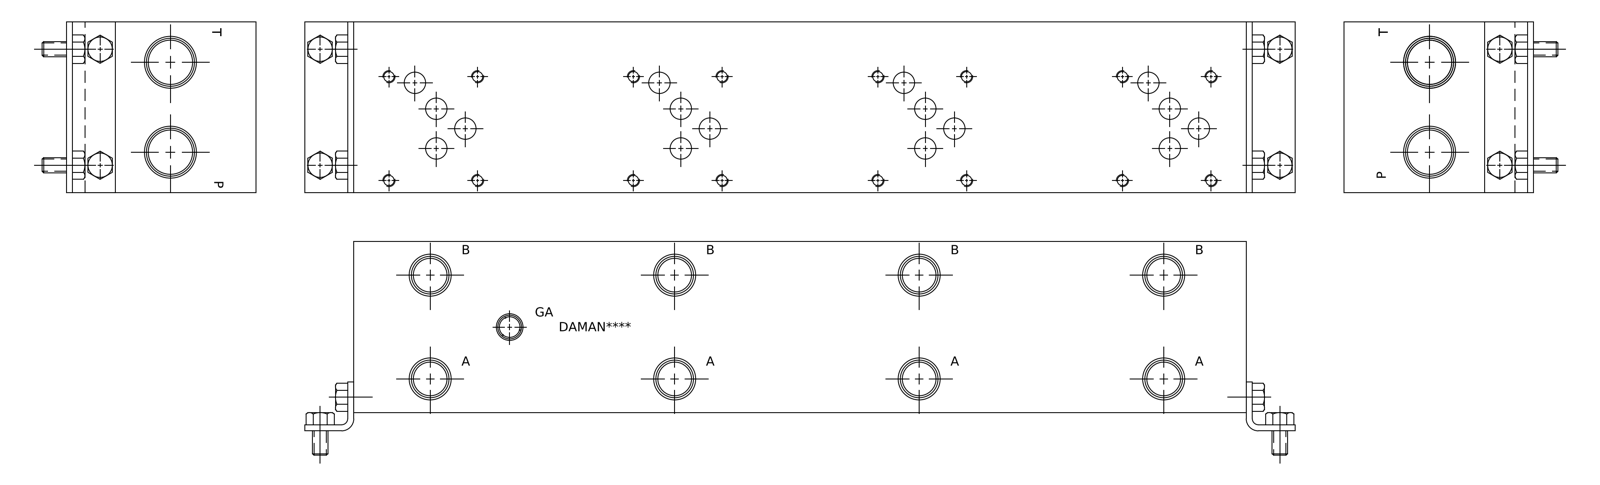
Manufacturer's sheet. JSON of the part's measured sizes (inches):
{"step_written_by": "Autodesk Inventor 2019 (AUTOMOTIVE_DESIGN)", "units": "inches", "bodies": {"solids": 1, "faces": 719, "planar": 420, "cylindrical": 82, "other": 217}, "overall_size": [18.25, 3.5, 3.5], "volume_in3": 216.7, "surface_area_in2": 321.6, "round_holes": [[0.201, 16], [0.25, 16], [0.438, 16], [0.688, 8], [0.85, 8], [0.257, 2], [0.312, 2], [0.906, 2], [1.06, 2], [0.422, 1], [0.546, 1]], "face_to_face_distances": [3.5, 18.25, 0.605, 2.895, 0.624, 17.626, 17.002, 0.039, 0.566, 3.461], "hole_center_spacings": [5, 10, 5.433, 2.793, 1.813, 4.209, 4.868, 5.432]}
